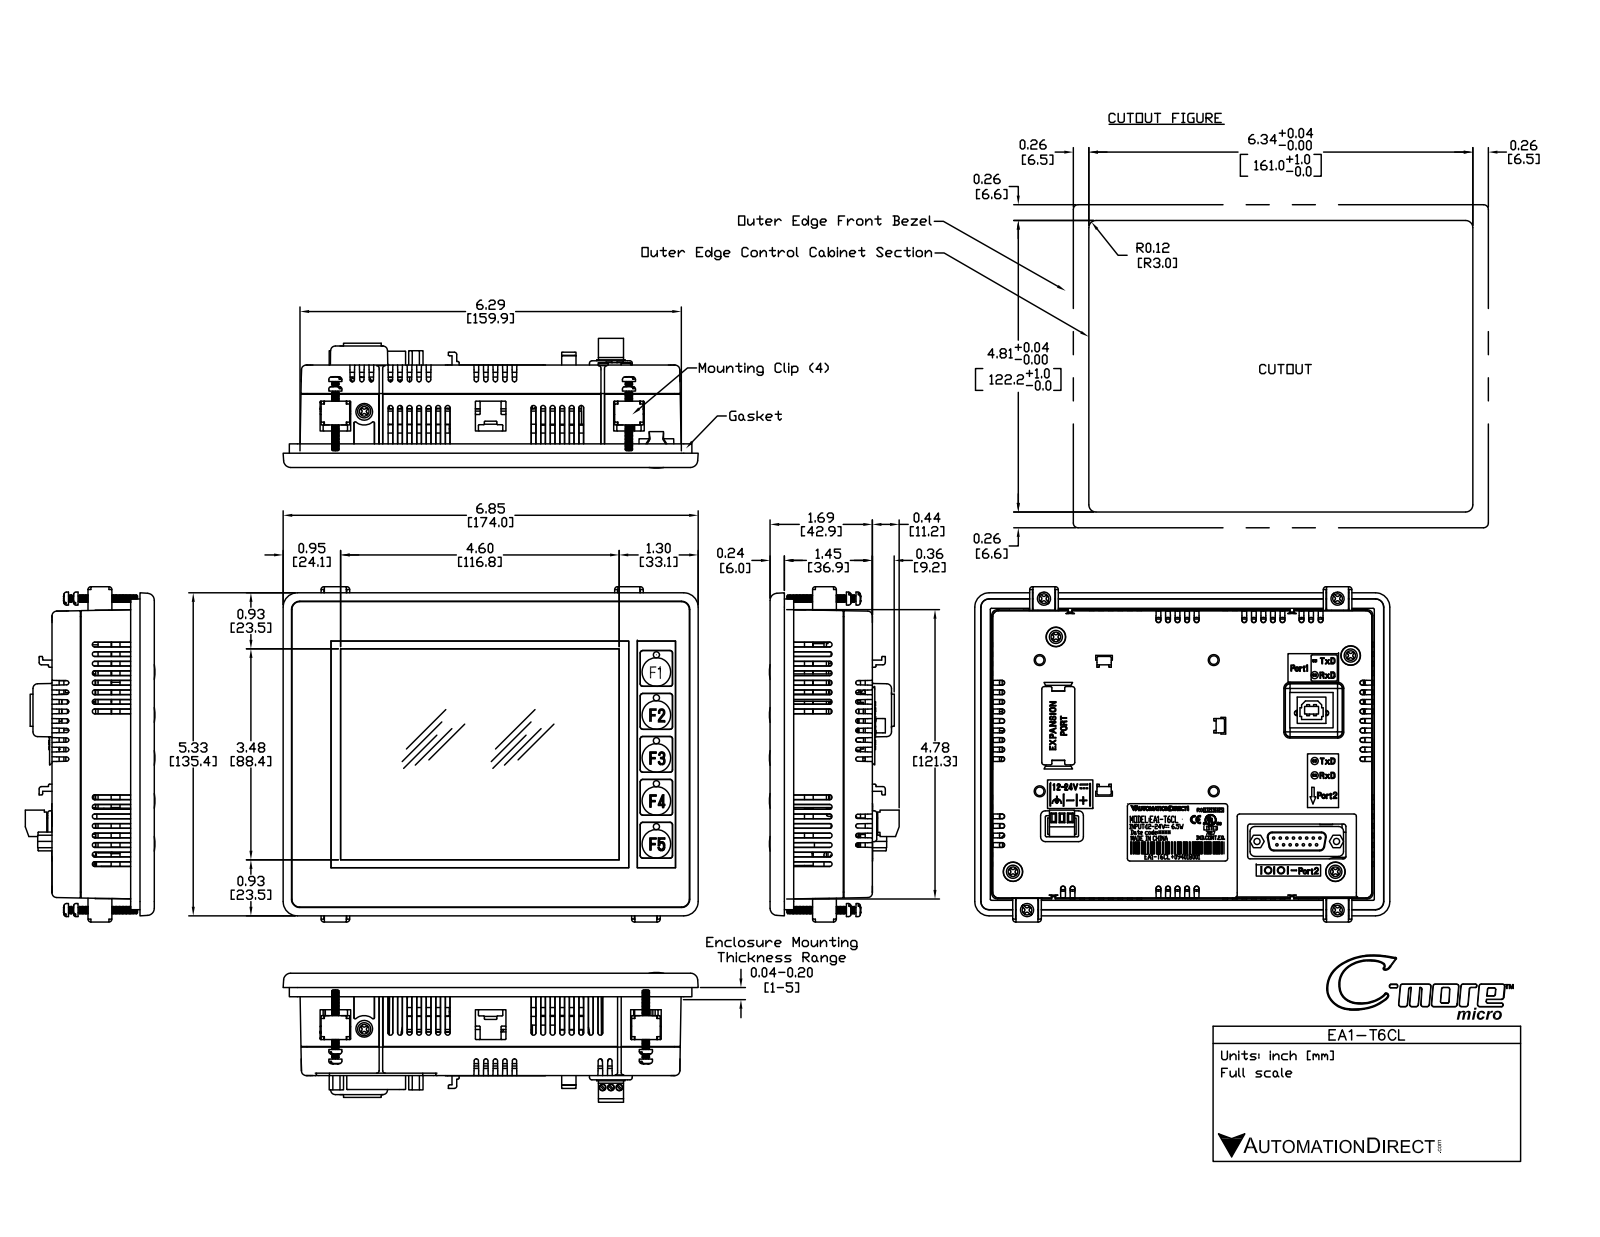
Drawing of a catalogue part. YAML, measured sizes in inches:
part_name: "EA1-T6CL"
step_written_by: "SolidWorks 2009 (CONFIG_CONTROL_DESIGN)"
units: inches
bodies: {solids: 19, faces: 656, planar: 465, cylindrical: 163, other: 28}
overall_size: [6.85, 5.331, 2.063]
volume: 43.14
surface_area: 261.3
round_holes:
  - {diameter: 0.091, count: 5}
  - {diameter: 0.433, count: 5}
  - {diameter: 0.315, count: 4}
  - {diameter: 0.271, count: 1}
round_bosses_or_shafts:
  - {diameter: 0.209, count: 5}
partial_cylinders:
  - {radius: 0.039, count: 34}
  - {radius: 0.079, count: 16}
  - {radius: 0.098, count: 8}
  - {radius: 0.02, count: 4}
  - {radius: 0.157, count: 4}
  - {radius: 0.157, count: 4}
  - {radius: 0.236, count: 4}
face_to_face_distances: [0.118, 1.571, 0.354, 0.472, 1.689, 4.657, 4.303, 4.185, 6.177, 5.823]
hole_center_spacings: [0.717, 1.433, 0.276, 0.441, 0.992, 2.15, 1.157, 1.709]
